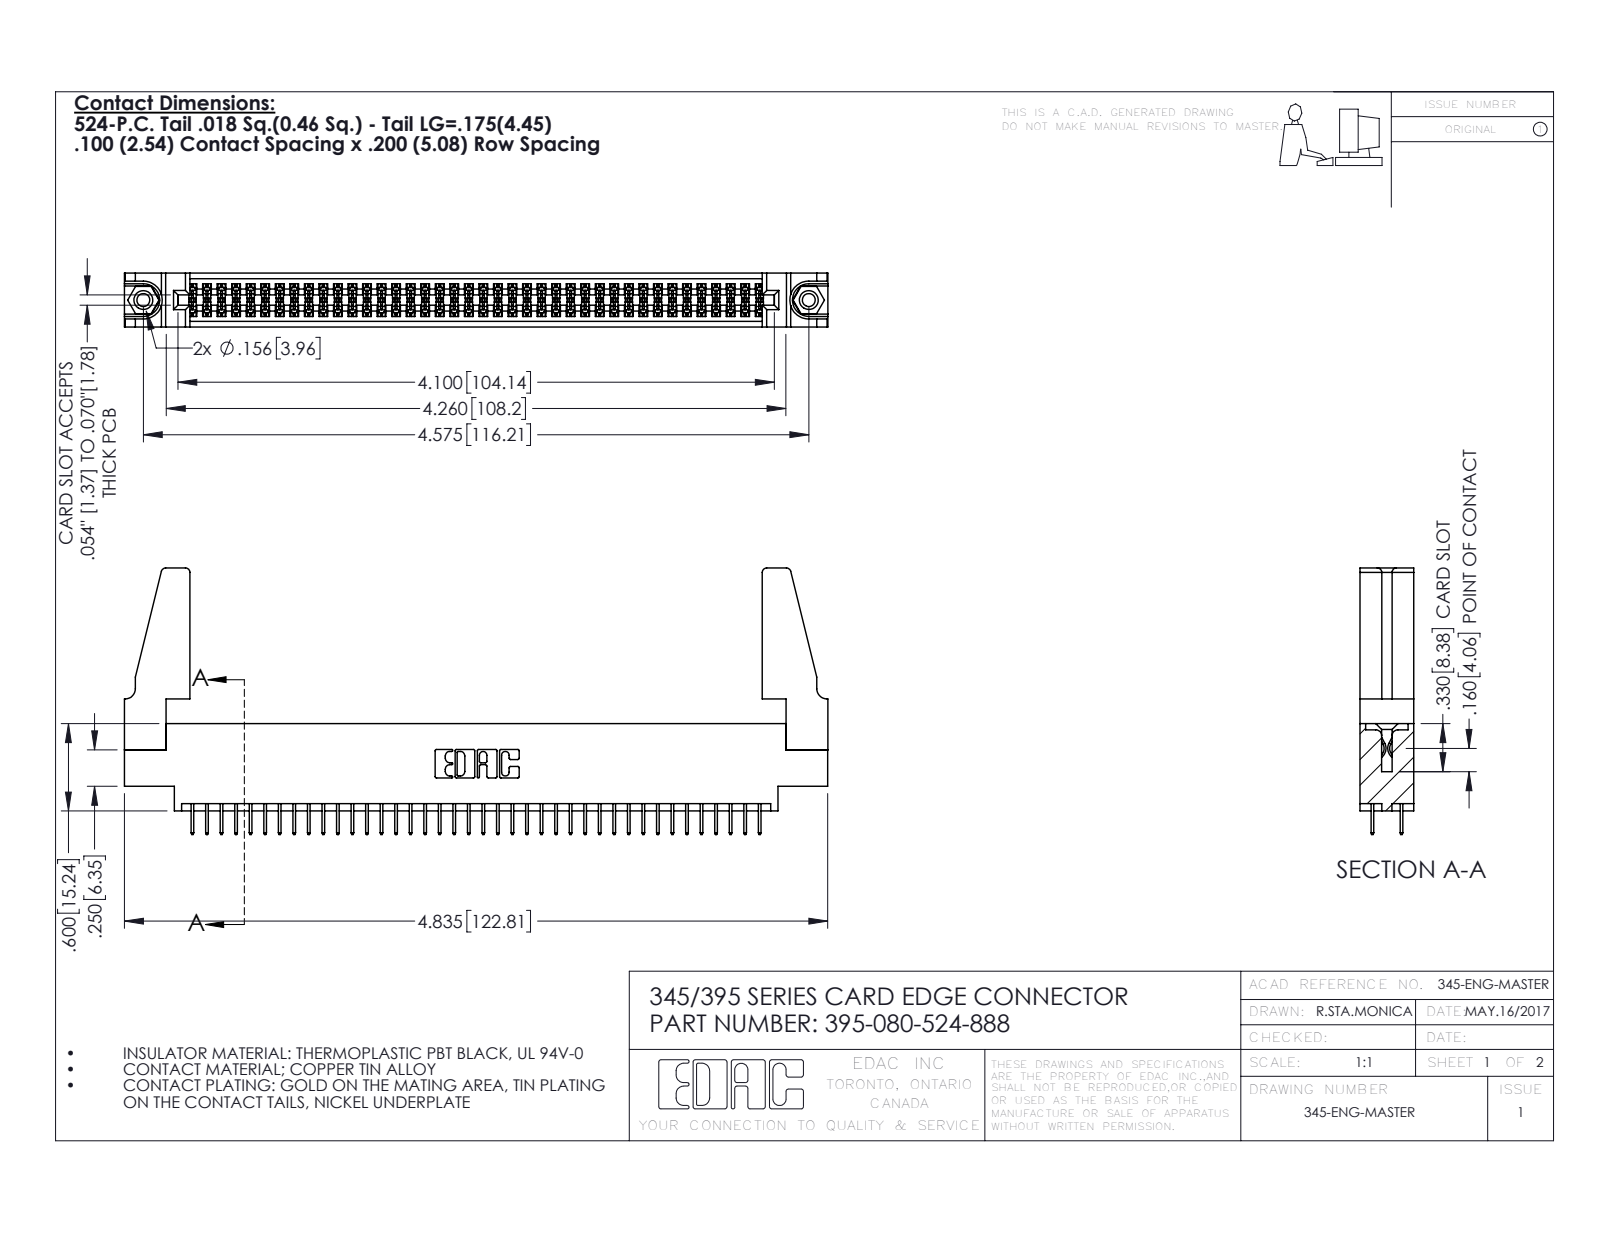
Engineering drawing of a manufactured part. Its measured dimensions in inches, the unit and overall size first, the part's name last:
Units: inches
Overall size (bounding box): 4.836 × 1.832 × 0.37
Round holes (diameter × count): ⌀0.089 ×2, ⌀0.125 ×2, ⌀0.156 ×2, ⌀0.064 ×1
Round bosses / shafts (diameter × count): ⌀0.155 ×2
Partial cylindrical surfaces — rounded edges, fillets, slot ends (radius × count): R0.006 ×120, R0.01 ×22, R0.03 ×8, R0.007 ×6, R0.031 ×6, R0.026 ×3, R0.014 ×2, R0.019 ×2
Main face-to-face distances: 0.072, 0.298, 0.37, 0.2, 0.098, 0.272, 0.025, 0.225, 0.175, 0.072
Hole centre spacings: 0.27, 4.339, 4.575
Volume: 0.911 in³ · Surface area: 31.27 in²
Bodies: 85 solids, 4574 faces (3276 planar, 1282 cylindrical, 16 other)
Part name (STEP PRODUCT): 345-292-001_345-293-124; 345-250-001_345-250-001-102; 395-080-524-888; 345-220-078_345-220-088 (+1 more)
STEP written by: SolidWorks 2016 (CONFIG_CONTROL_DESIGN)
